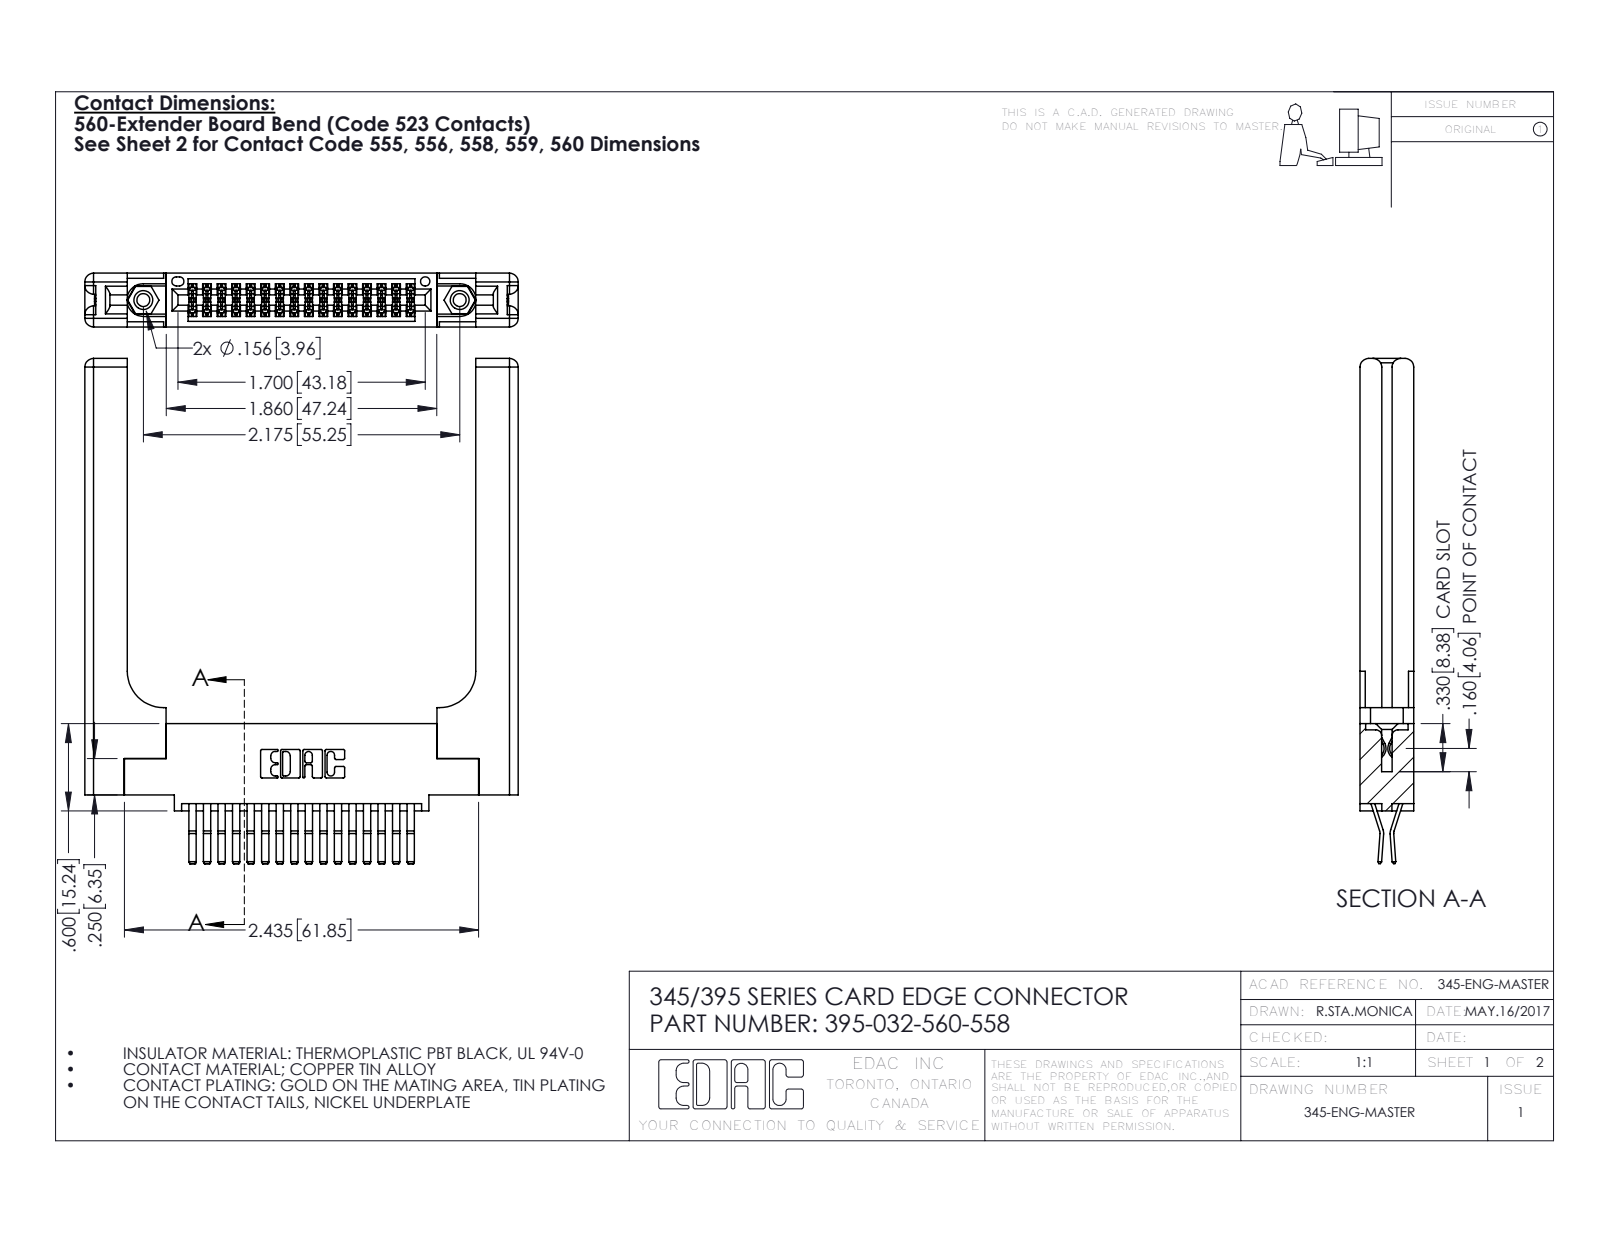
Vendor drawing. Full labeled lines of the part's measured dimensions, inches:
Part name (STEP PRODUCT): 345 Part_0.110 Offset - 0.156 Dia-TH; 345-250-001_345-250-001-102; 345-292-001_560 Tail; 345-220-058_345-220-058 (+1 more)
STEP written by: SolidWorks 2016 (CONFIG_CONTROL_DESIGN)
Units: inches
Bodies: 37 solids, 2050 faces (1288 planar, 702 cylindrical, 60 other)
Overall size (bounding box): 3.472 × 2.979 × 0.37
Volume: 0.959 in³ · Surface area: 24.64 in²
Round holes (diameter × count): ⌀0.089 ×2, ⌀0.125 ×2, ⌀0.156 ×2, ⌀0.064 ×1
Round bosses / shafts (diameter × count): ⌀0.155 ×2
Partial cylindrical surfaces — rounded edges, fillets, slot ends (radius × count): R0.006 ×48, R0.01 ×22, R0.06 ×16, R0.007 ×6, R0.031 ×6, R0.026 ×3, R0.01 ×2, R0.014 ×2
Main face-to-face distances: 0.37, 0.072, 0.298, 0.025, 0.15, 0.148, 0.077, 0.22, 0.225, 0.098
Hole centre spacings: 0.27, 1.942, 2.175
